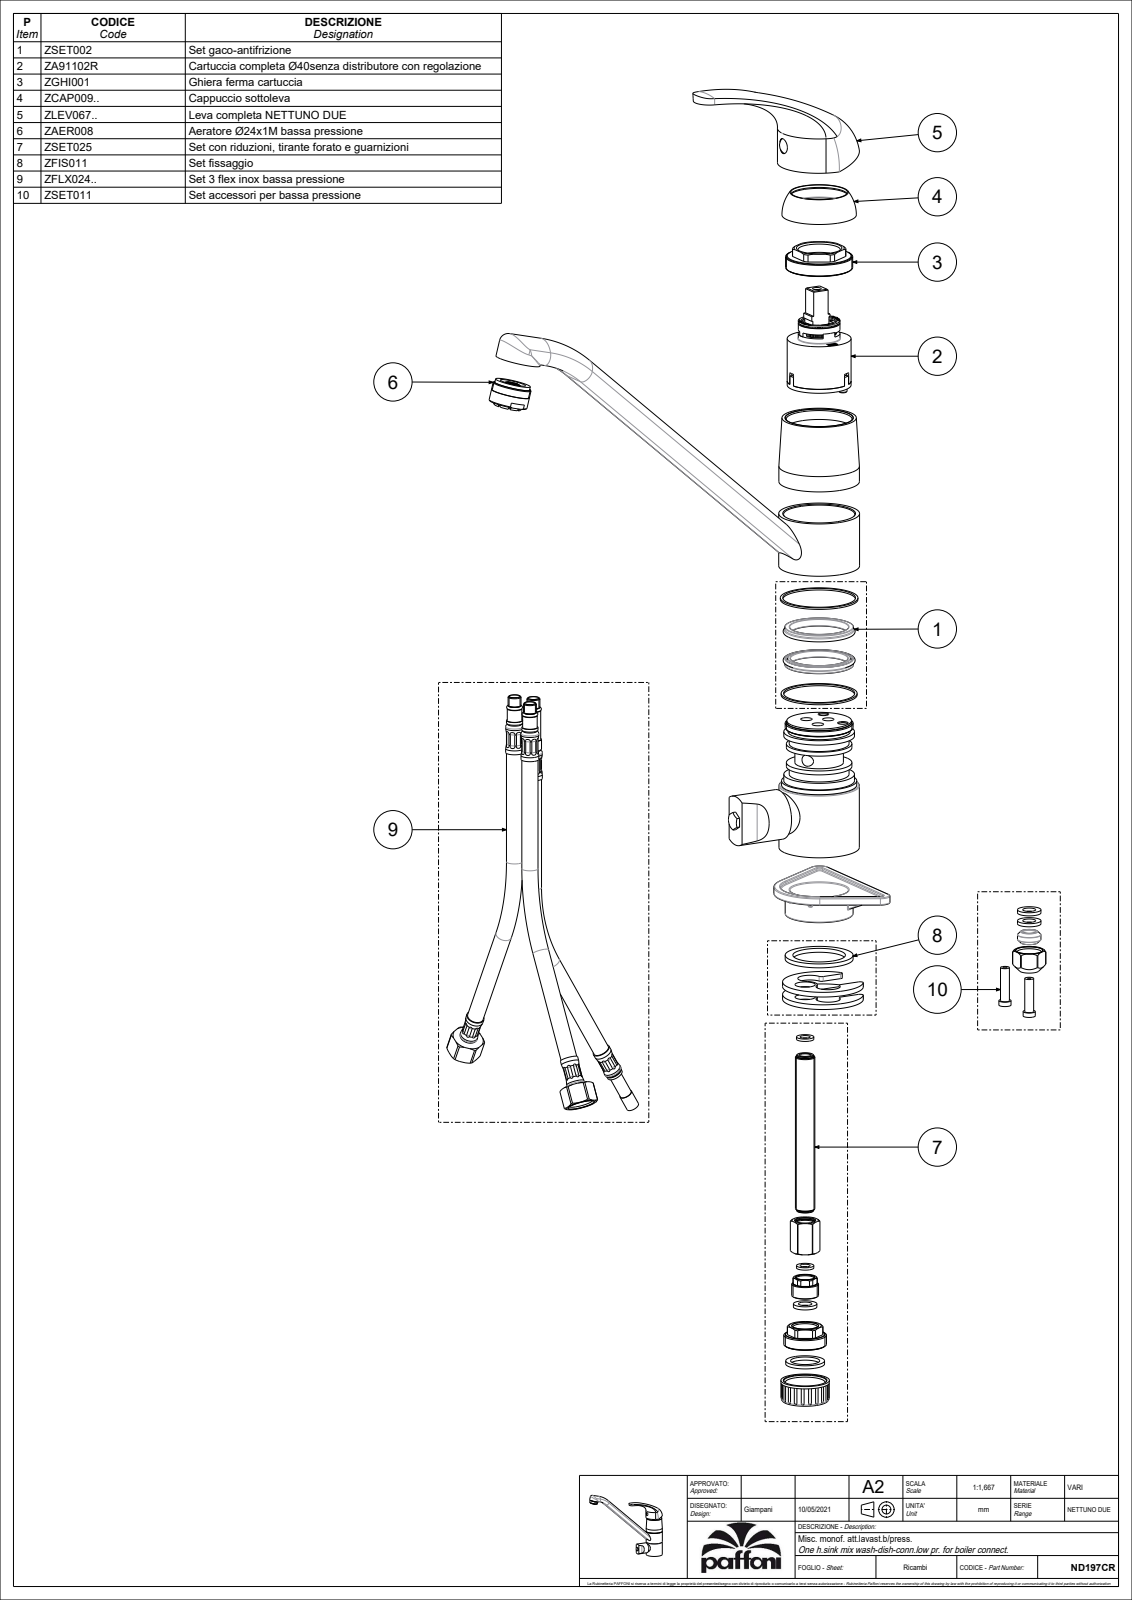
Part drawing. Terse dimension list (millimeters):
name: ND197CR
written by: CREO PARAMETRIC BY PTC INC, 2020044 (CONFIG_CONTROL_DESIGN)
unit: mm
bodies: 1 solid, 282 faces (96 planar, 97 cylindrical, 89 other)
size: 253.53 × 218.37 × 51
volume: 382 625 mm³; area: 68 073 mm²
holes: 7× ⌀7, 4× ⌀9, 3× ⌀8.5, 1× ⌀5.5, 1× ⌀6, 1× ⌀11, 1× ⌀16, 1× ⌀18.6, 1× ⌀21.5, 1× ⌀22, 1× ⌀24, 1× ⌀43
bosses: 2× ⌀5, 1× ⌀50, 1× ⌀49.8, 1× ⌀49.7, 1× ⌀46.5, 1× ⌀44.8, 1× ⌀43.7, 1× ⌀33
rounds: 4× R5.5, 2× R7, 2× R16.5, 1× R3.9, 1× R4, 1× R65
face distances: 129.7, 1, 128.7, 73.9, 72.9, 55.8, 31, 40.4, 39.4, 33.5
hole spacings: 9.96, 12.42, 16.1, 10, 11, 14.2, 19, 21
